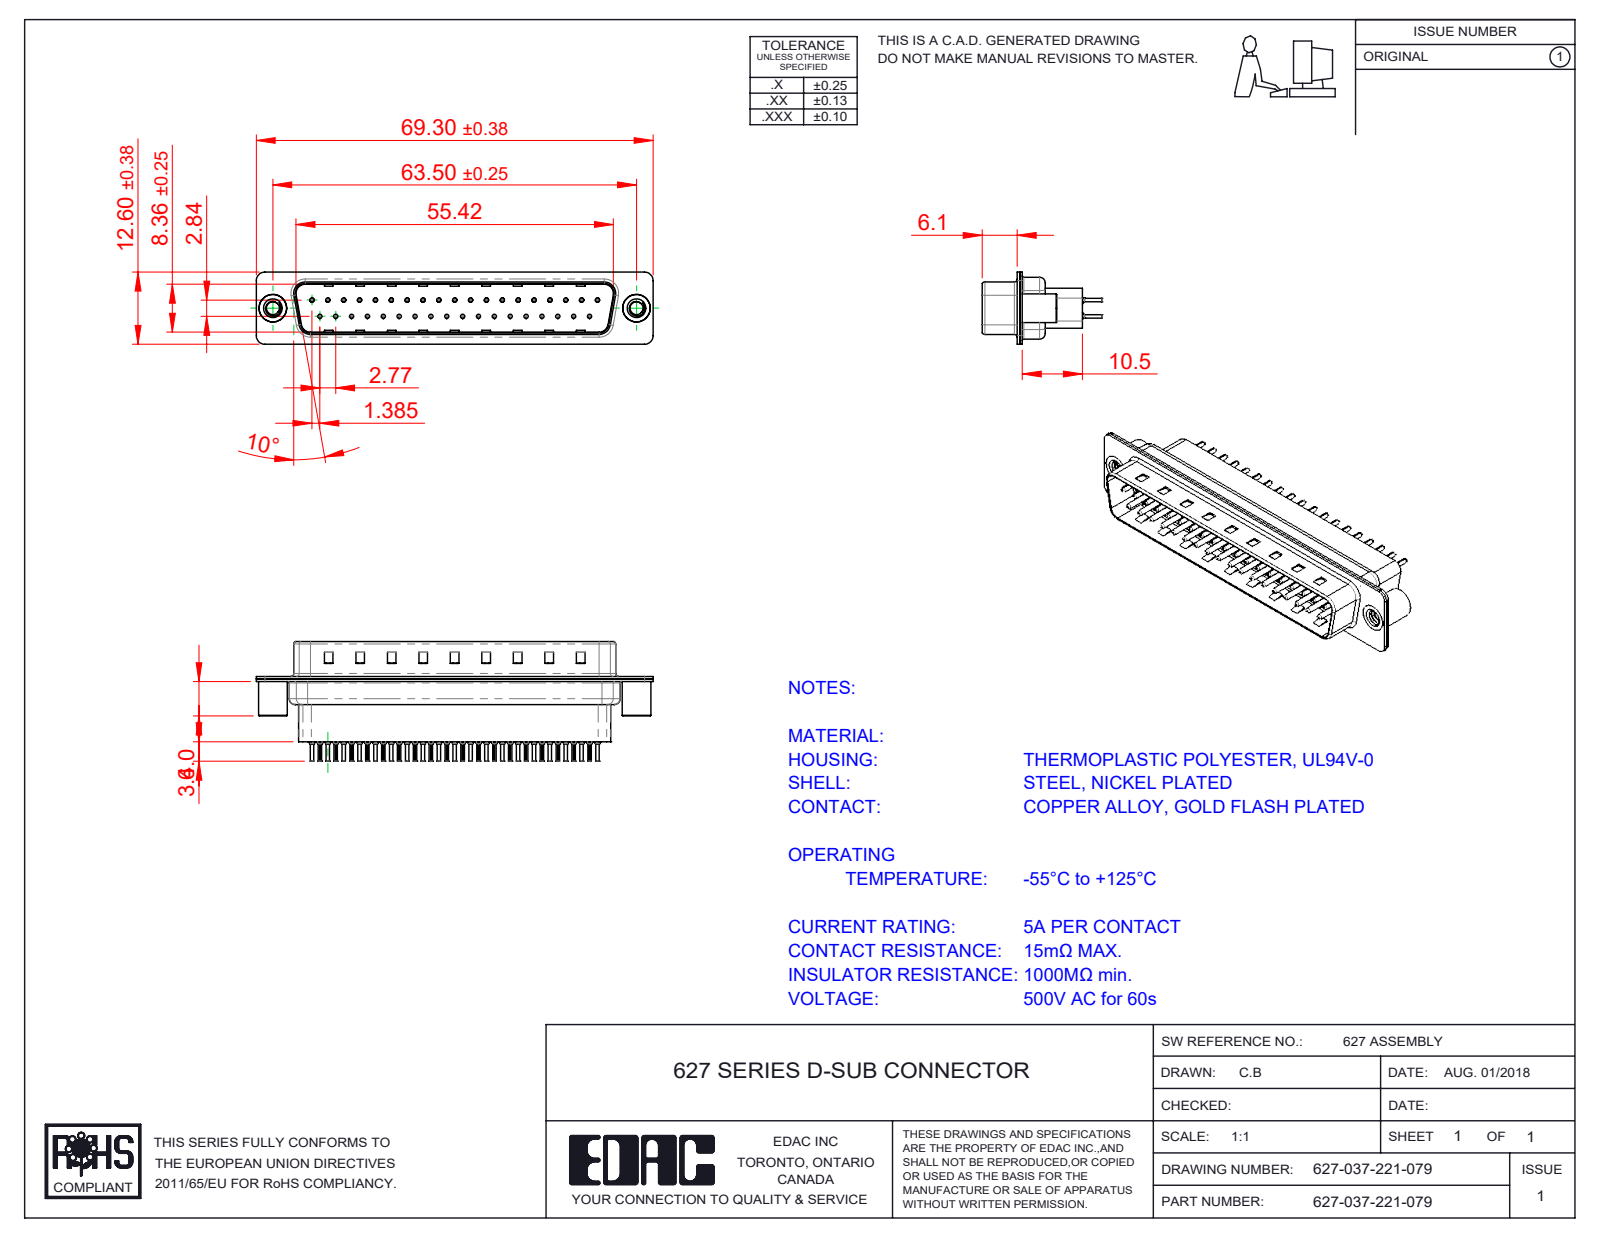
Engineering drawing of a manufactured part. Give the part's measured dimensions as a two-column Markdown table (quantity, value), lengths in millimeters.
| quantity | value |
| --- | --- |
| part name | 627 Shell Rear_37 Contacts; 627 Housing_37 HP; 627 4-40 Threaded Standoff BS; 627 Shell Front_37 Contacts (+3 more) |
| STEP written by | SolidWorks 2020 (CONFIG_CONTROL_DESIGN) |
| units | millimeters |
| bodies | 42 solids, 4060 faces (1091 planar, 1530 cylindrical, 1439 other) |
| overall size | 69.3 × 20.8 × 12.6 |
| volume | 5 403 mm³ |
| surface area | 13 750 mm² |
| round holes (diameter × count) | 0.2 × 37, 0.35 × 37, 1.1 × 37, 1.6 × 37, 2.26 × 2, 4 × 2, 4.8 × 2 |
| round bosses / shafts (diameter × count) | 2 × 37, 1.5 × 37, 0.75 × 37, 0.6 × 37, 5 × 2, 4.9 × 2 |
| partial cylindrical surfaces (radius × count) | 0.1 × 74, 1.5 × 16, 2 × 12, 0.5 × 8, 1.6 × 8, 0.25 × 4, 0.6 × 4, 0.65 × 4 |
| main face-to-face distances | 0.4, 0.82, 9.58, 0.68, 7.68, 0.45, 1.5, 1.08, 8.08, 8.76 |
| hole center spacings | 3.16, 2.77, 5.54, 8.31, 5.04, 10.1, 11.08, 12.78 |
